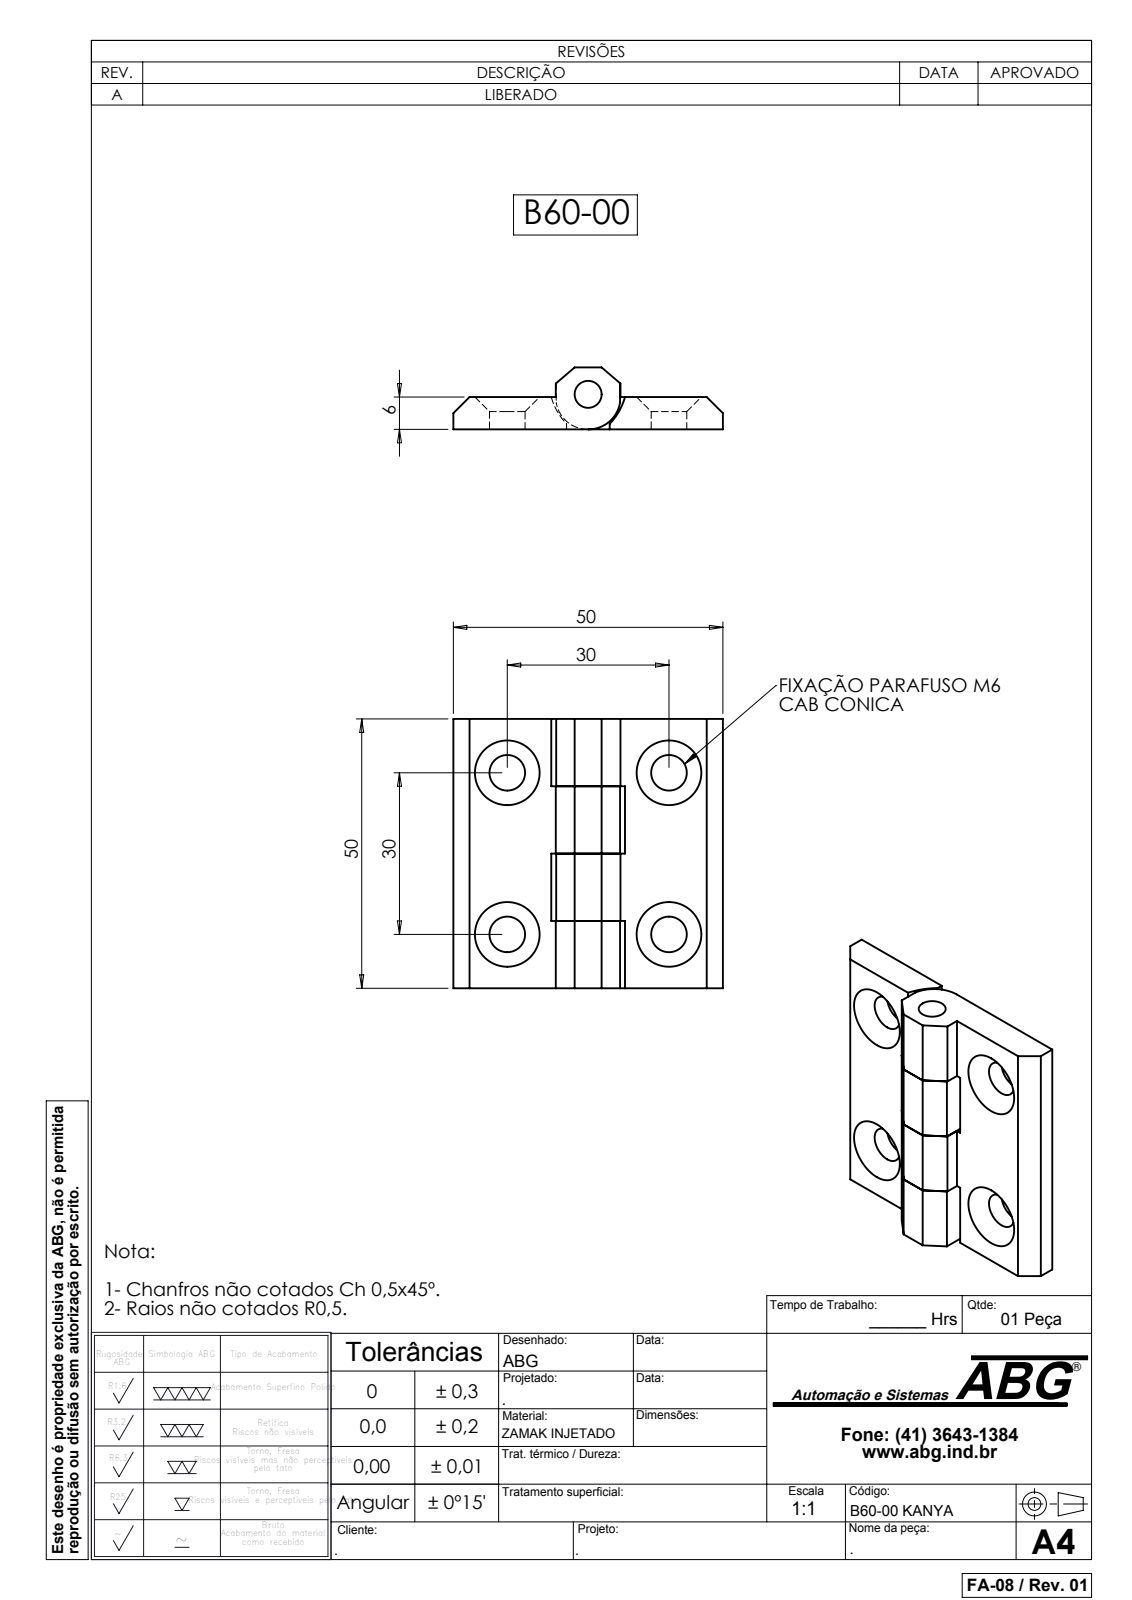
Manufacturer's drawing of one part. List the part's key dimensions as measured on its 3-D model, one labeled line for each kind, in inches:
Part name (STEP PRODUCT): KANYA B60-00; B60-00 KANYA
STEP written by: SolidWorks 2007 (CONFIG_CONTROL_DESIGN)
Units: inches
Bodies: 2 solids, 74 faces (42 planar, 24 cylindrical, 8 other)
Overall size (bounding box): 1.969 × 1.969 × 0.453
Volume: 0.911 in³ · Surface area: 13.17 in²
Round holes (diameter × count): ⌀0.26 ×4, ⌀0.197 ×1
Partial cylindrical surfaces — rounded edges, fillets, slot ends (radius × count): R0.234 ×2, R0.459 ×2
Main face-to-face distances: 0.236, 0.492, 0.984, 1.969, 1.476, 0.453, 0.217, 0.748, 1.22, 0.751
Hole centre spacings: 1.181, 1.67
